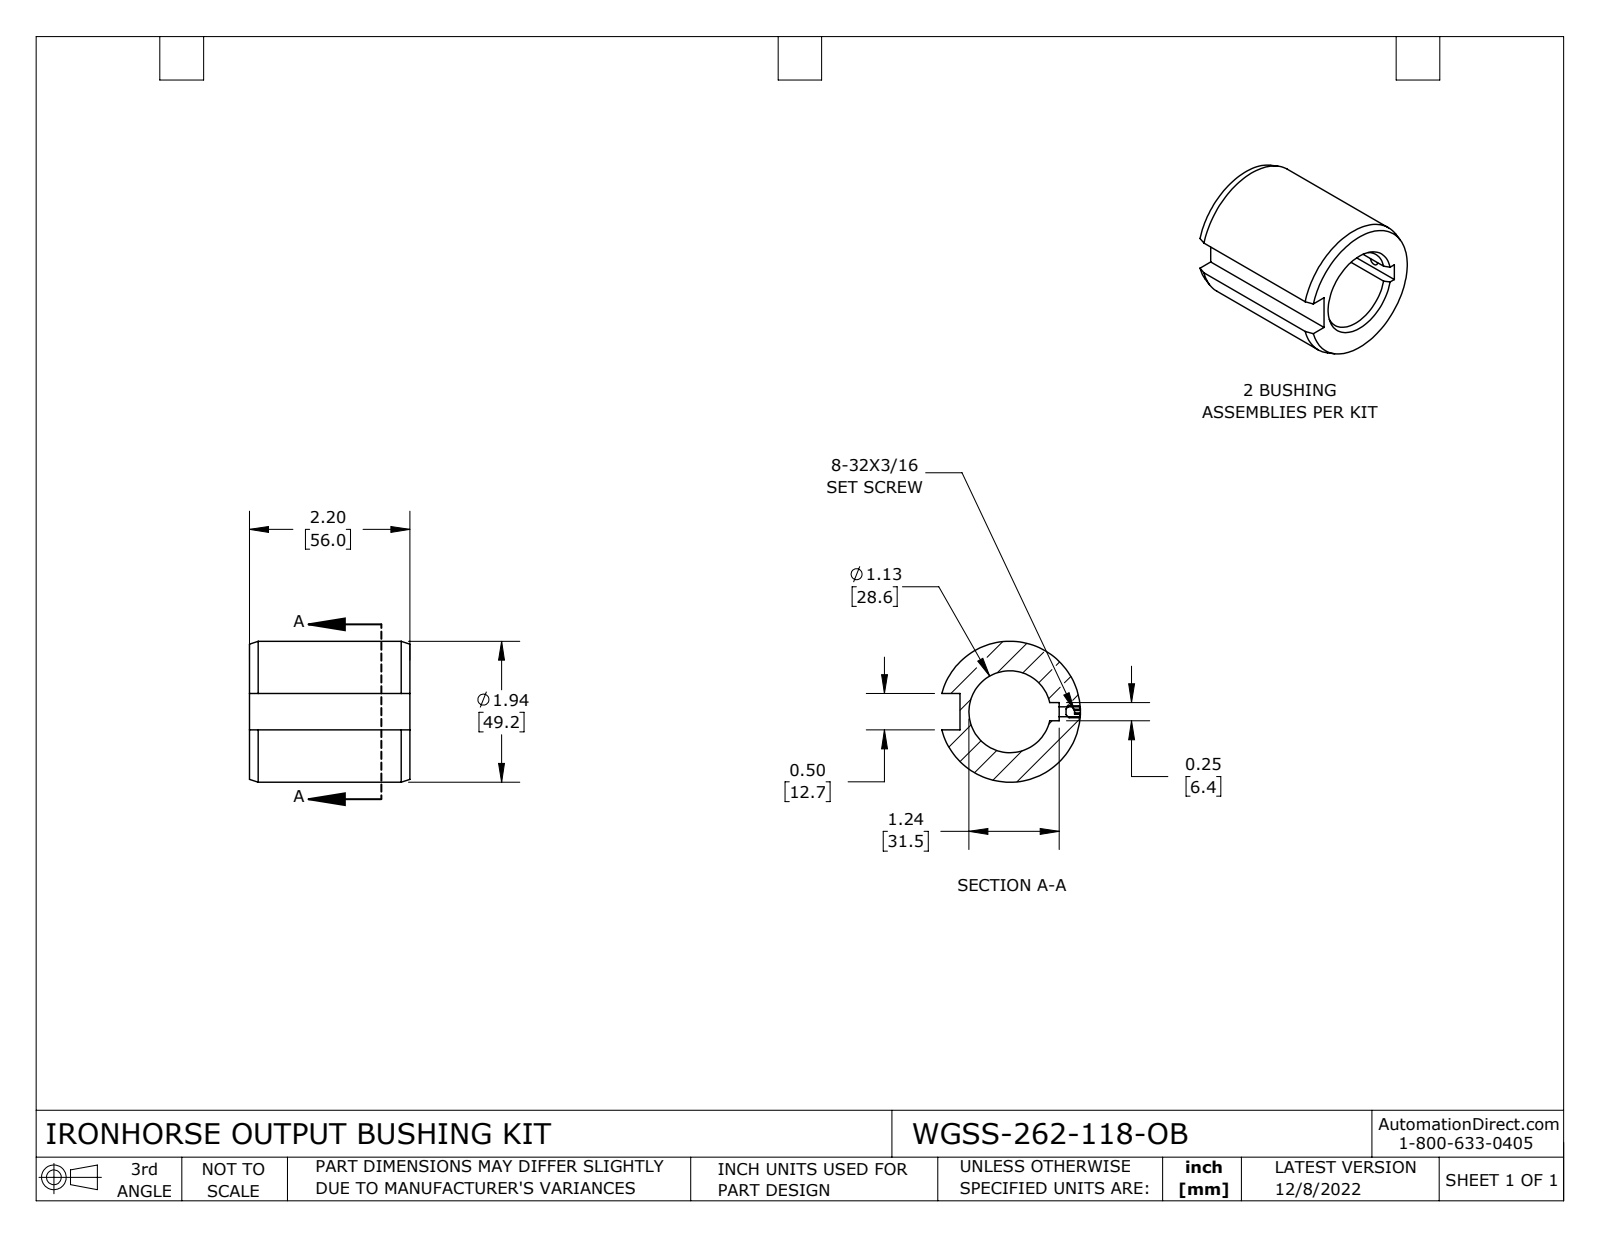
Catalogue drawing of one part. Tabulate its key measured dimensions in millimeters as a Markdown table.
| quantity | value |
| --- | --- |
| part name | WGSS-262-118-OB |
| STEP written by | SolidWorks 2021 (CONFIG_CONTROL_DESIGN) |
| units | millimeters |
| bodies | 2 solids, 41 faces (17 planar, 10 cylindrical, 14 other) |
| overall size | 56 × 49.21 × 48.38 |
| volume | 63 974 mm³ |
| surface area | 16 817 mm² |
| round holes (diameter × count) | 3.45 × 1, 28.58 × 1 |
| round bosses / shafts (diameter × count) | 49.21 × 1, 4.16 × 1 |
| main face-to-face distances | 56, 3.18, 9.52, 12.7, 34.65, 6.34, 1.5, 2.38, 37.03, 5 |
